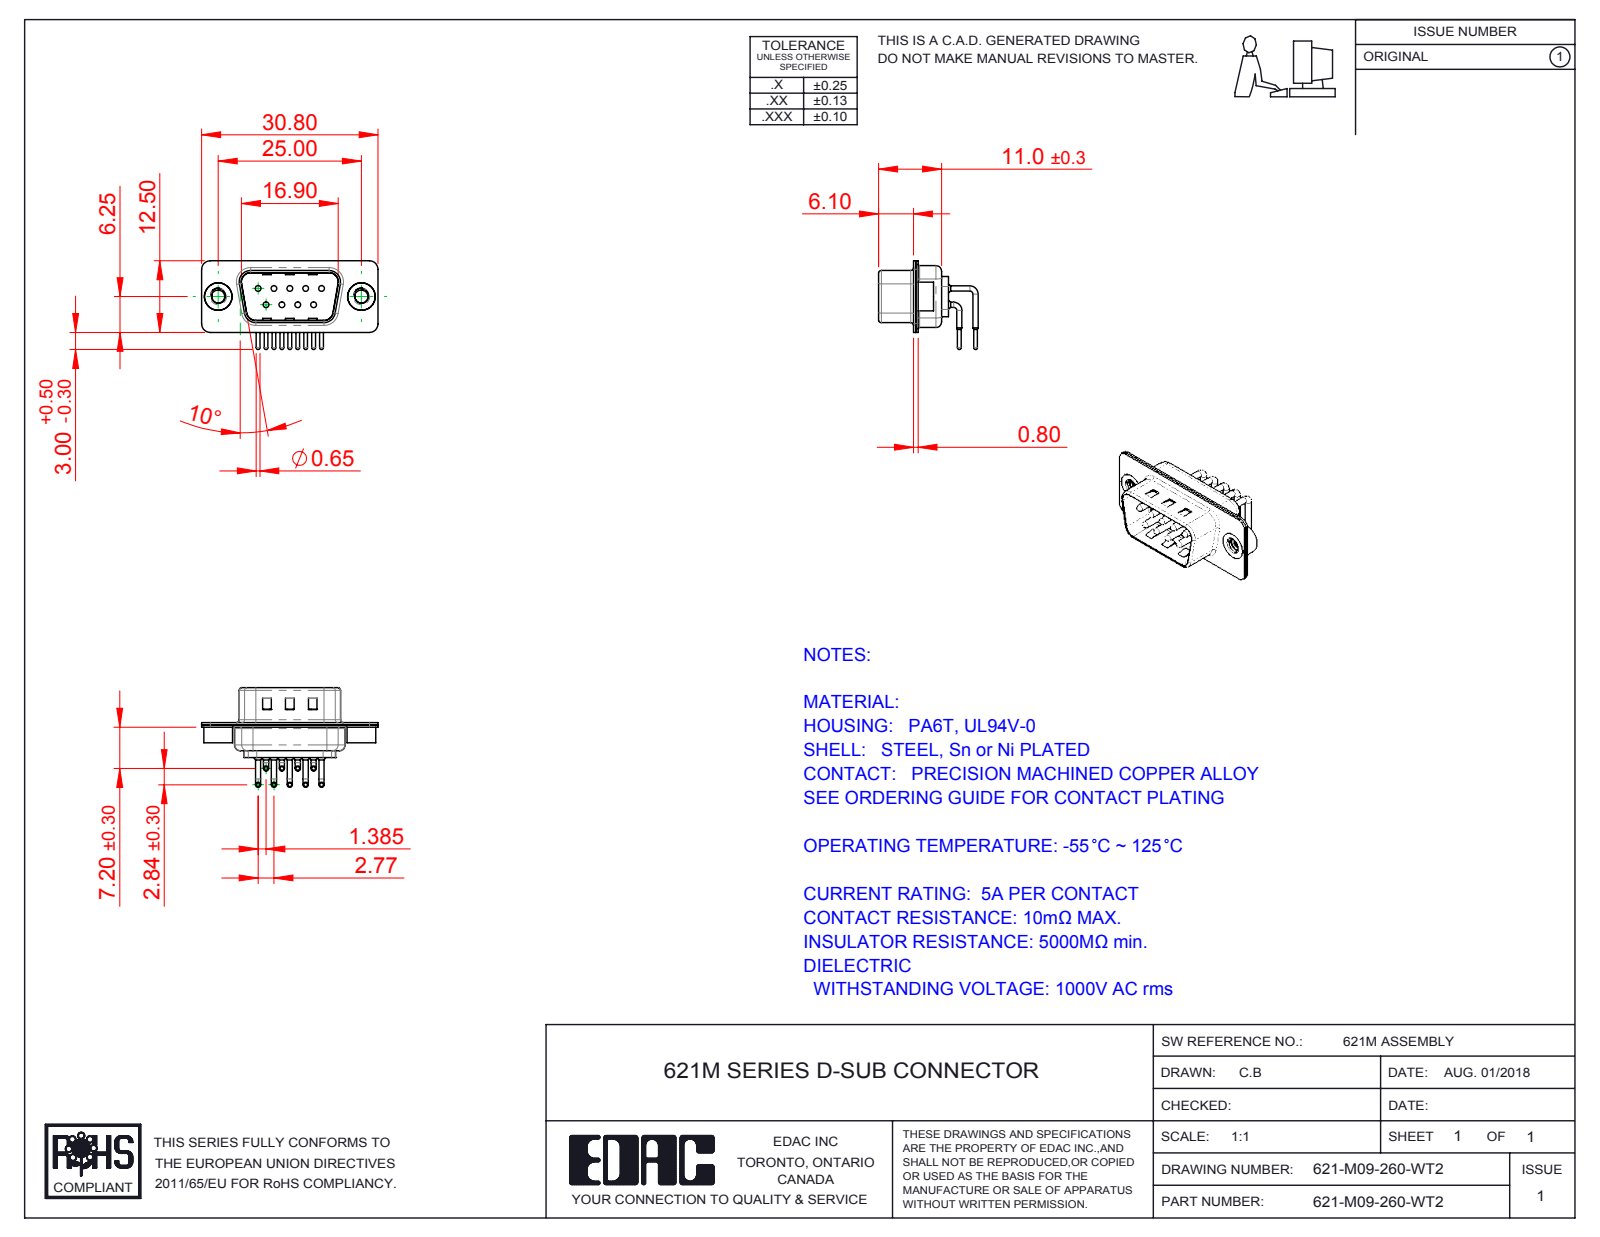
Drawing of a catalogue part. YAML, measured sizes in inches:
part_name: "621M Housing_09 Contacts; 621-M09-260-WT2; 621M Shell Rear_09 Contacts; 621M Contact Row 1 (+3 more)"
step_written_by: "SolidWorks 2016 (CONFIG_CONTROL_DESIGN)"
units: inches
bodies: {solids: 14, faces: 1294, planar: 683, cylindrical: 453, other: 158}
overall_size: [1.213, 0.685, 0.61]
volume: 0.083
surface_area: 5.969
round_holes:
  - {diameter: 0.039, count: 9}
  - {diameter: 0.067, count: 9}
  - {diameter: 0.079, count: 9}
  - {diameter: 0.089, count: 2}
  - {diameter: 0.157, count: 2}
  - {diameter: 0.189, count: 2}
round_bosses_or_shafts:
  - {diameter: 0.035, count: 18}
  - {diameter: 0.059, count: 9}
  - {diameter: 0.026, count: 9}
  - {diameter: 0.197, count: 2}
  - {diameter: 0.193, count: 2}
partial_cylinders:
  - {radius: 0.059, count: 16}
  - {radius: 0.079, count: 12}
  - {radius: 0.04, count: 9}
  - {radius: 0.02, count: 8}
  - {radius: 0.063, count: 8}
  - {radius: 0.01, count: 4}
  - {radius: 0.024, count: 4}
  - {radius: 0.026, count: 4}
face_to_face_distances: [0.016, 0.033, 0.031, 0.376, 0.049, 0.409, 0.343, 0.014, 0.24, 0.224]
hole_center_spacings: [0.124, 0.109, 0.218, 0.198, 0.198, 0.327, 0.28, 0.294]
